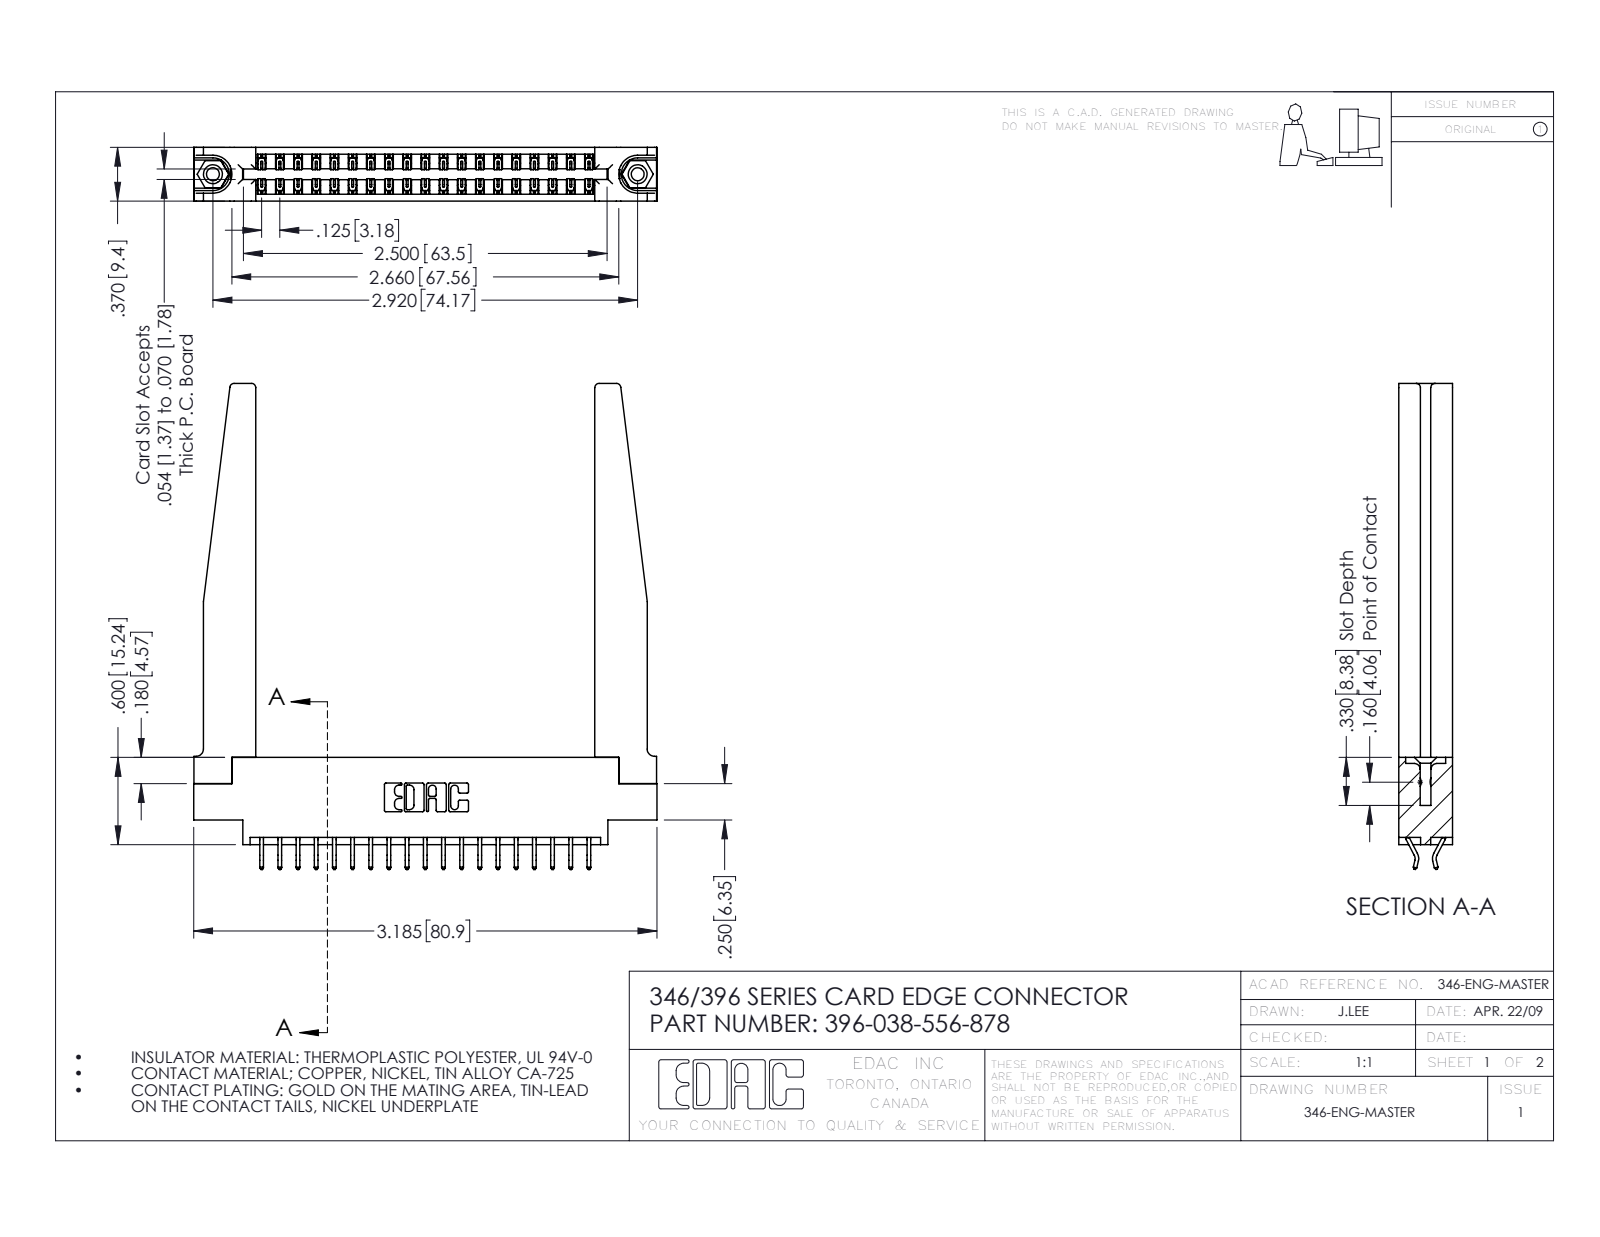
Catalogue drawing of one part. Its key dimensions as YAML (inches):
part_name: "346 Part_0.170 Offset - 0.156 Dia-TH; 345-250-001_345-250-001-102; 396-038-556-878; 345-292-001_556 Tail (+1 more)"
step_written_by: "SolidWorks 2016 (CONFIG_CONTROL_DESIGN)"
units: inches
bodies: {solids: 43, faces: 2564, planar: 1704, cylindrical: 808, other: 52}
overall_size: [3.34, 3.185, 0.37]
volume: 0.883
surface_area: 25.89
round_holes:
  - {diameter: 0.089, count: 2}
  - {diameter: 0.125, count: 2}
  - {diameter: 0.156, count: 2}
  - {diameter: 0.064, count: 1}
round_bosses_or_shafts:
  - {diameter: 0.155, count: 2}
partial_cylinders:
  - {radius: 0.006, count: 57}
  - {radius: 0.01, count: 22}
  - {radius: 0.03, count: 8}
  - {radius: 0.007, count: 6}
  - {radius: 0.031, count: 6}
  - {radius: 0.05, count: 4}
  - {radius: 0.026, count: 3}
  - {radius: 0.01, count: 2}
face_to_face_distances: [0.37, 0.048, 0.322, 0.072, 0.148, 0.15, 0.25, 0.025, 0.298, 0.275]
hole_center_spacings: [0.246, 2.713, 2.92]
